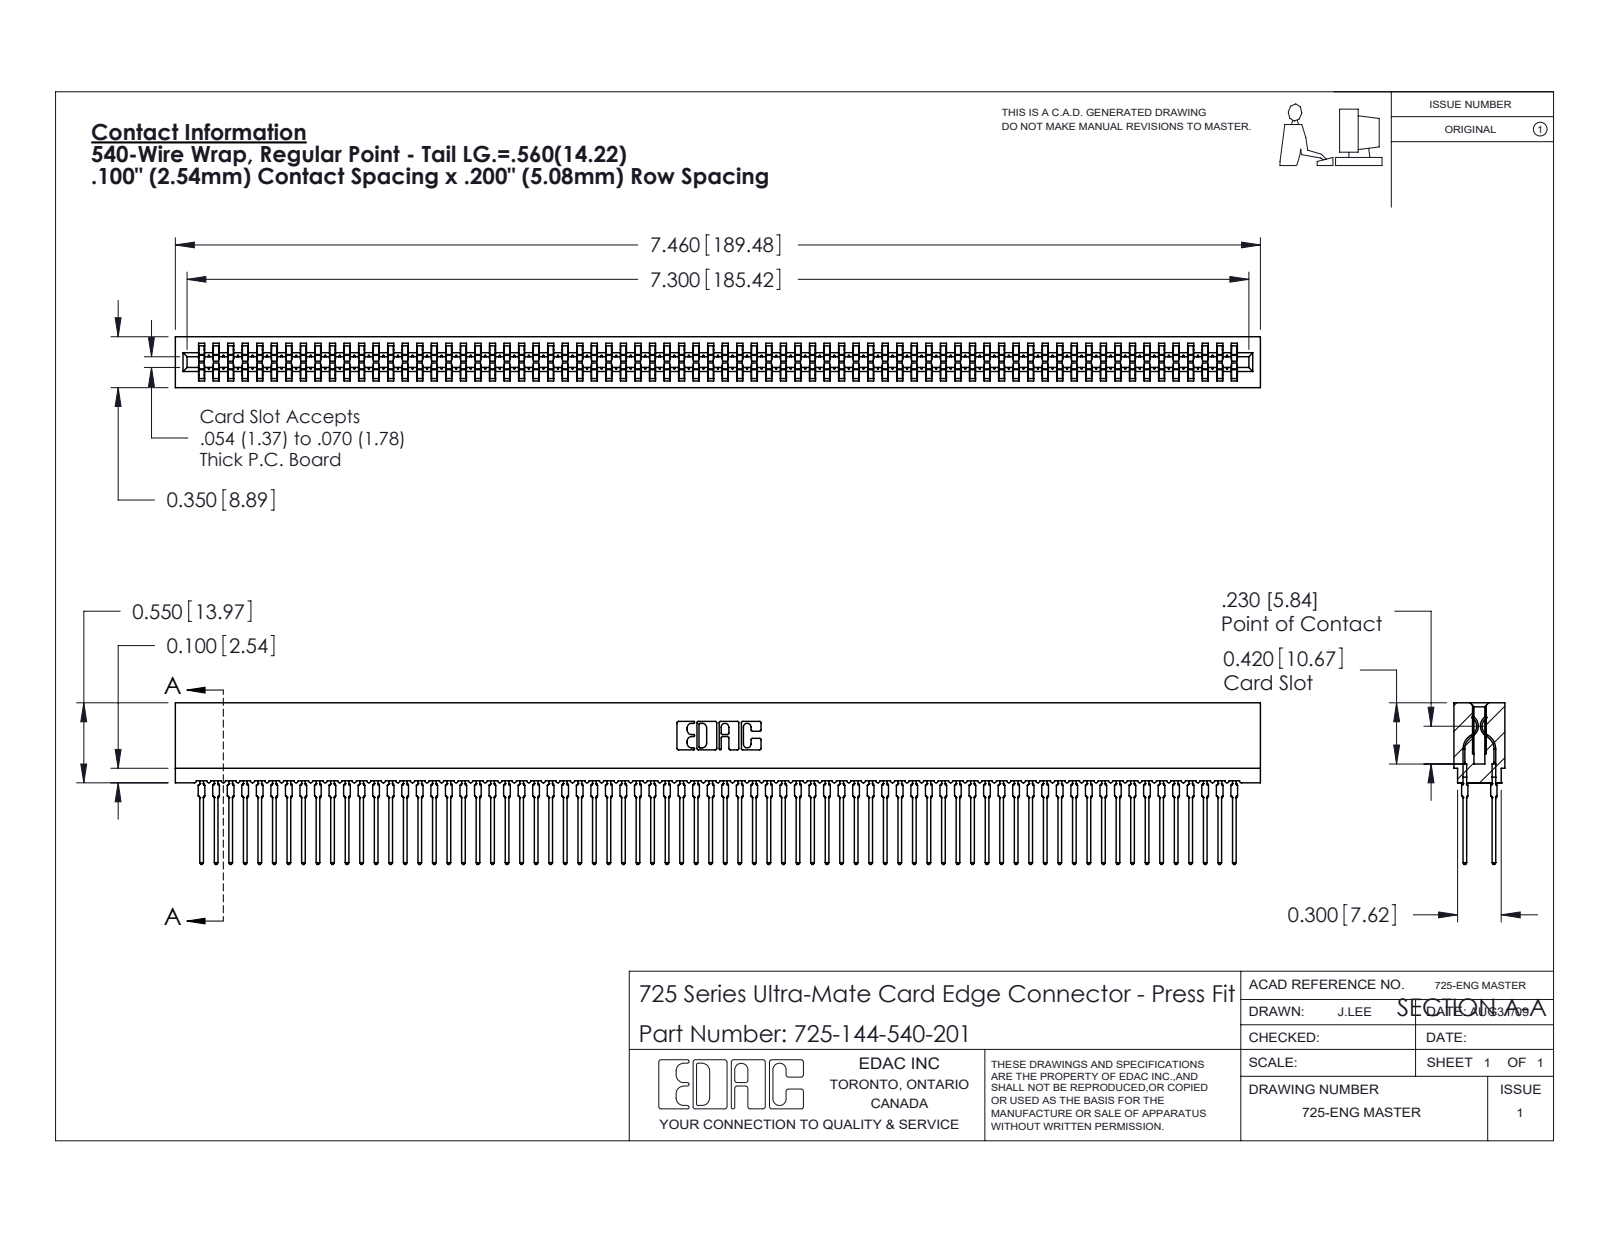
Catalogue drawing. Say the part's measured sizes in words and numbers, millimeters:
The part is named "745-292-001_540; 725 Part_Insulator Option - 01; 725-144-540-201". Its 3-D file was written by "SolidWorks 2020 (CONFIG_CONTROL_DESIGN)". It is 145 solids with 12983 faces: 6679 planar, 2560 cylindrical and 3744 other. Overall it measures 189.5 by 28.2 by 8.9 millimeters. Its volume is 15 300 cubic millimeters and its surface area 34 630 square millimeters. Partial cylindrical surfaces (rounded edges, fillets, slot ends): 288 of radius 0.5, 144 of radius 0.4, 22 of radius 0.3, 8 of radius 0.1, 8 of radius 0.3, 6 of radius 0.2, 6 of radius 0.8, 3 of radius 0.7. The main face-to-face distances are 1.6, 7.3, 5.1, 8.9, 5.4, 3.5, 1.9, 3.8, 2.2, 6.7.
